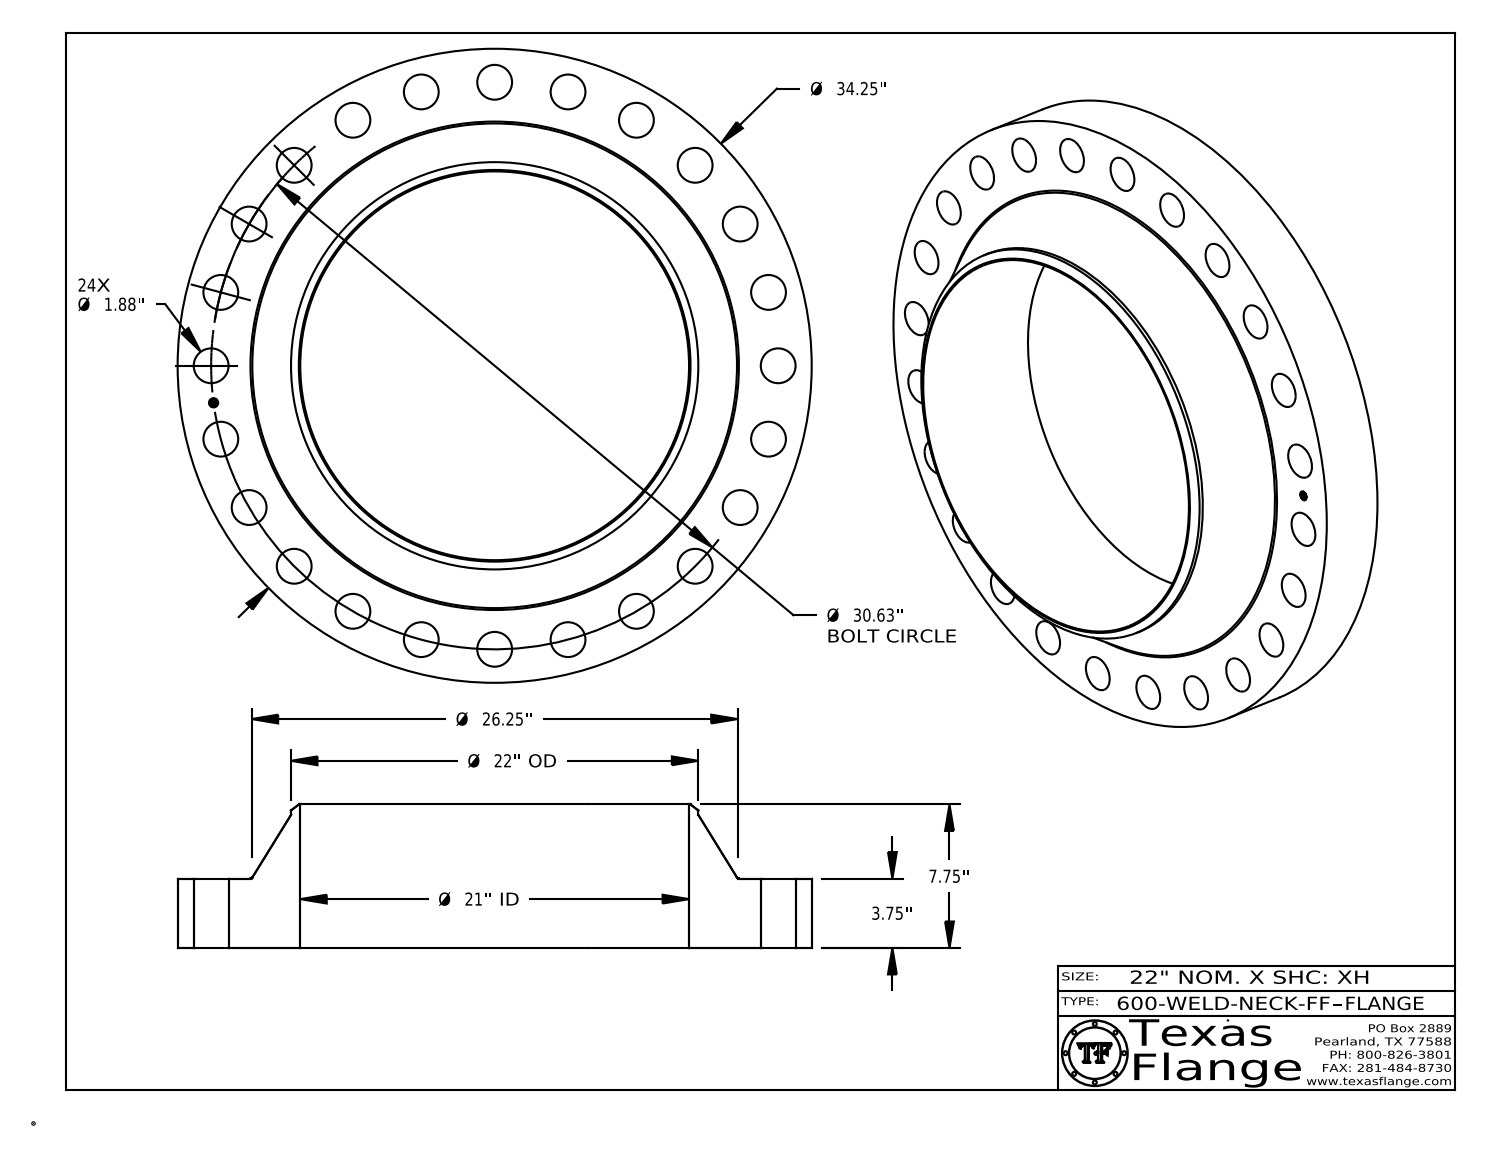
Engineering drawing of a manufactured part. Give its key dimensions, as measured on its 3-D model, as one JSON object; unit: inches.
{"part_name": "600-WELD-NECK-FF", "step_written_by": "CATIA V5 STEP AP214 (AUTOMOTIVE_DESIGN)", "units": "inches", "bodies": {"solids": 1, "faces": 448, "planar": 368, "cylindrical": 74, "other": 6}, "overall_size": [34.25, 34.25, 7.75], "volume_in3": 2306, "surface_area_in2": 2631, "round_holes": [[1.88, 24], [0.495, 1], [21, 1]], "round_bosses_or_shafts": [[0.03, 8], [34.25, 1], [22, 1], [0.39, 1]], "face_to_face_distances": [3.75, 7.75, 4, 0.015, 3.735, 4.015, 0.148, 0.145, 0.027, 0.096], "hole_center_spacings": [15.315, 3.998, 11.722, 24.3, 7.928, 18.646, 28.298, 30.368]}
